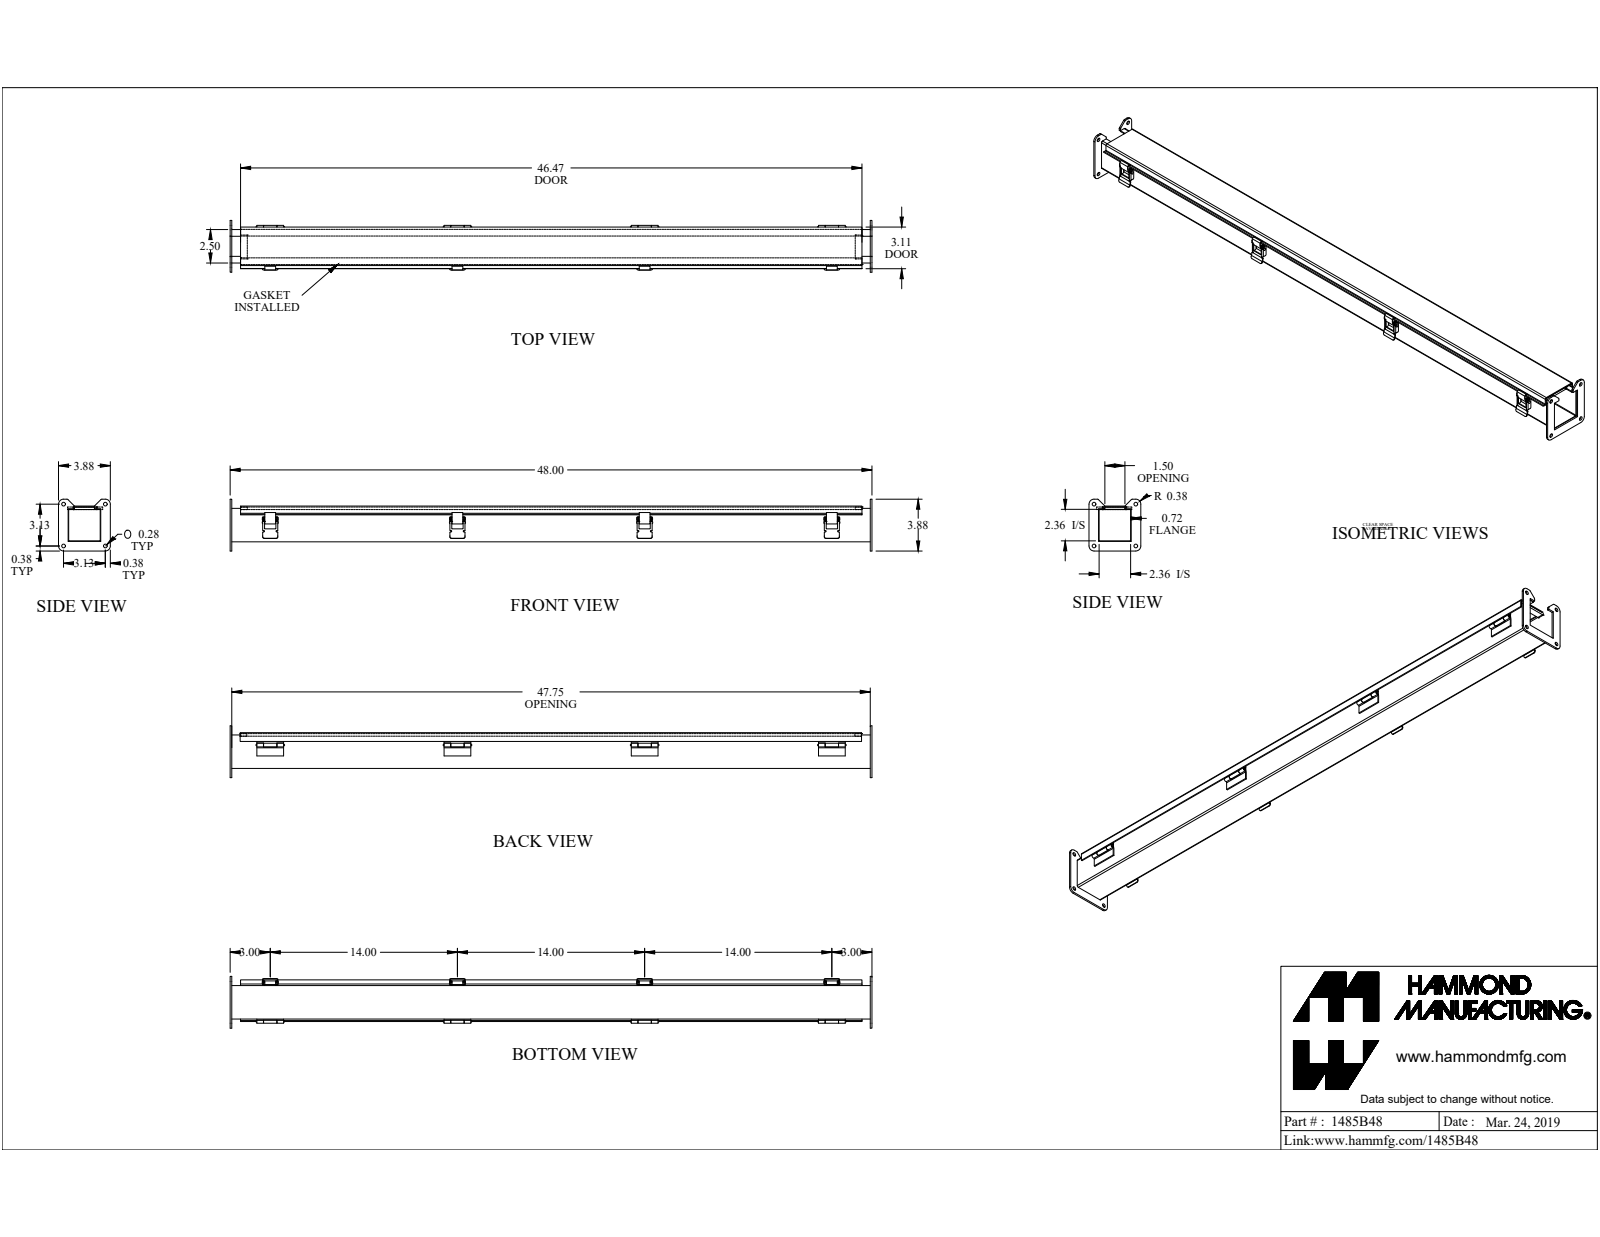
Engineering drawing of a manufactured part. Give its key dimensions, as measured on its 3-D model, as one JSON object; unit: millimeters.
{"part_name": "1485B48", "step_written_by": "SolidWorks 2019 (CONFIG_CONTROL_DESIGN)", "units": "millimeters", "bodies": {"solids": 32, "faces": 640, "planar": 378, "cylindrical": 238, "other": 24}, "overall_size": [1219.2, 98.4, 98.4], "volume_mm3": 898300, "surface_area_mm2": 917400, "round_holes": [[7.1, 4], [3.2, 1], [4.2, 1]], "round_bosses_or_shafts": [[7, 1], [4.1, 1], [4, 1], [3.2, 1], [3.2, 1]], "partial_cylinders_radius": [[0.7, 16], [2.2, 16], [3.2, 13], [0.4, 8], [1.2, 8], [0.9, 7], [2.7, 7], [9.5, 4]], "face_to_face_distances": [1.8, 61.7, 66, 63.5, 59.8, 67.9, 64.2, 4.4, 66.4, 4.7], "hole_center_spacings": [79.4, 112.3, 27.3, 27.9, 51.5, 52.4, 74.3, 80.6]}
